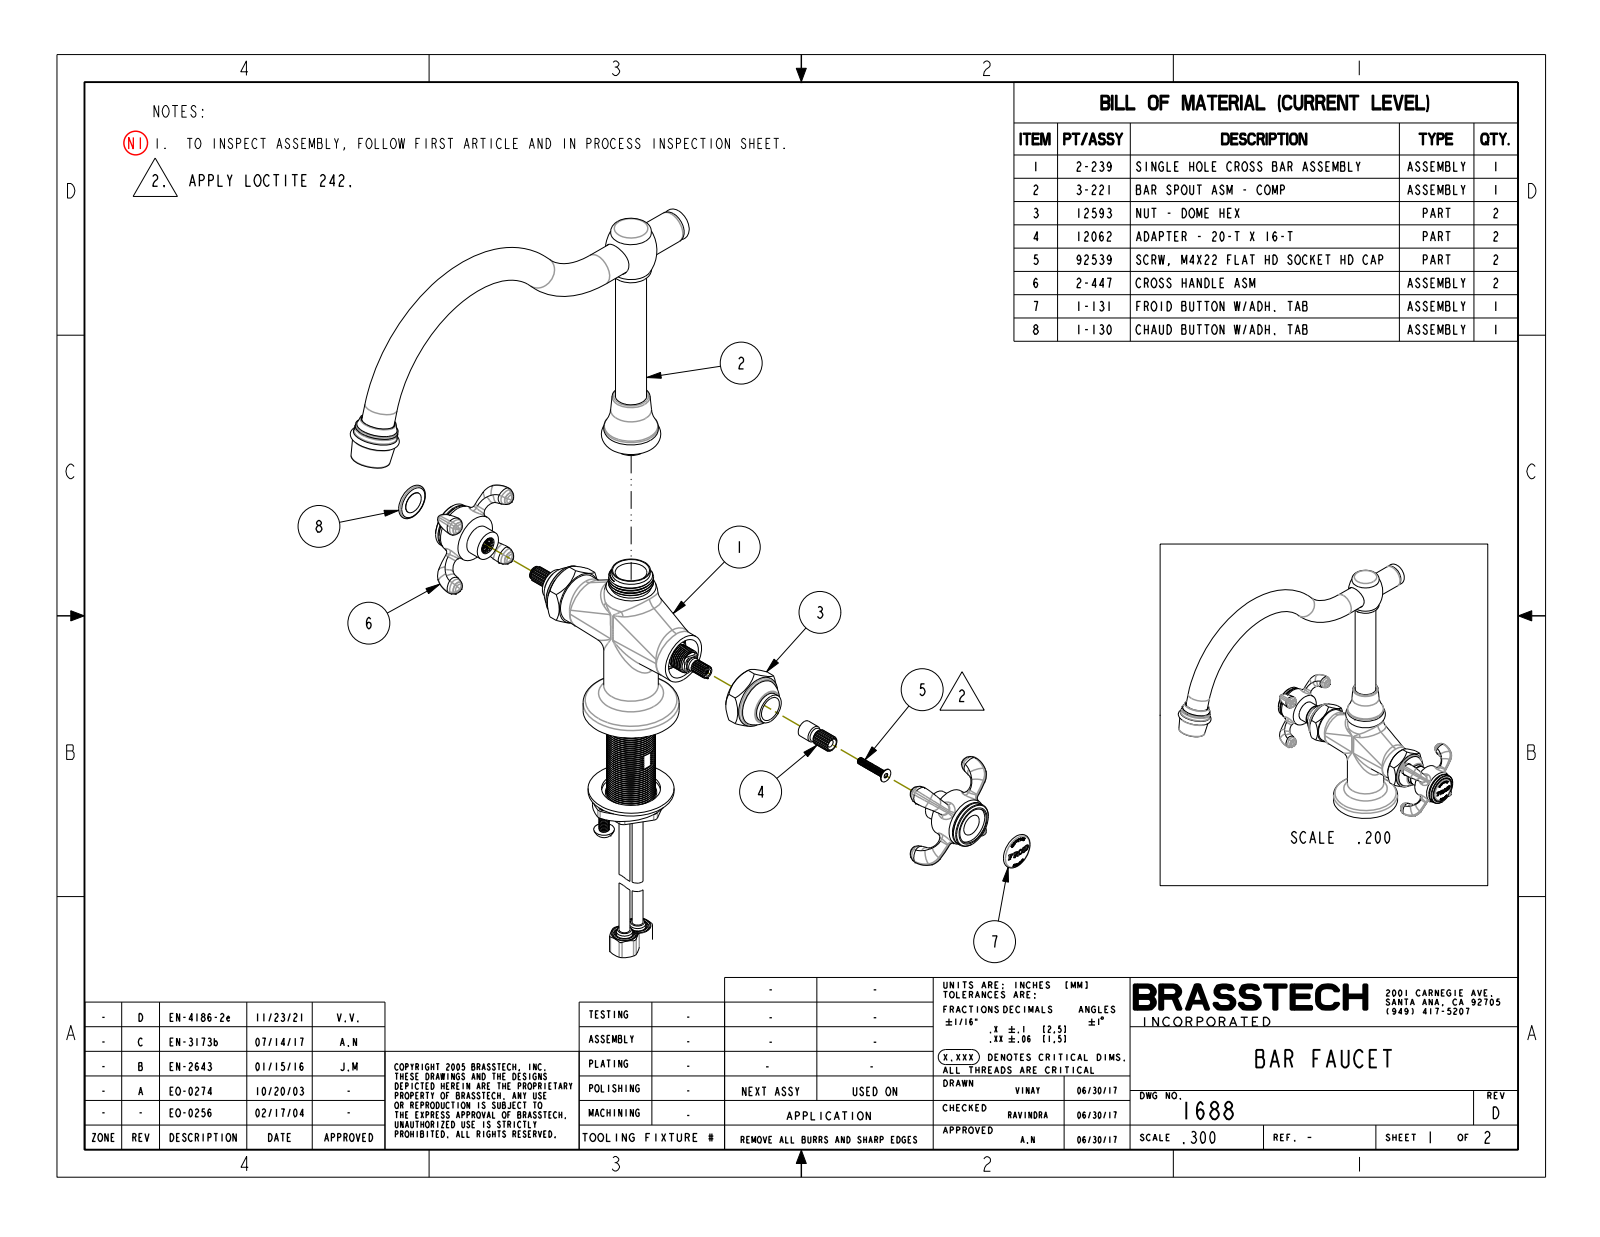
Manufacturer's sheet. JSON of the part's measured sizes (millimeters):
{"part_name": "1688_WEB", "step_written_by": "PRO/ENGINEER BY PARAMETRIC TECHNOLOGY CORPORATION, 2009300 (CONFIG_CONTROL_DESIGN)", "units": "millimeters", "bodies": {"solids": 0, "faces": 770, "planar": 31, "cylindrical": 135, "other": 604}, "overall_size": [285.3, 266.5, 192.3], "round_holes": [[19.4, 1]], "round_bosses_or_shafts": [[19.1, 2], [55.9, 1], [31.8, 1], [31.7, 1], [30.9, 1], [29.7, 1], [28.3, 1], [26.8, 1]], "face_to_face_distances": [11.9, 95.8, 40.3, 52.2, 136, 148, 88.4, 83.8, 107.7, 31.8]}
